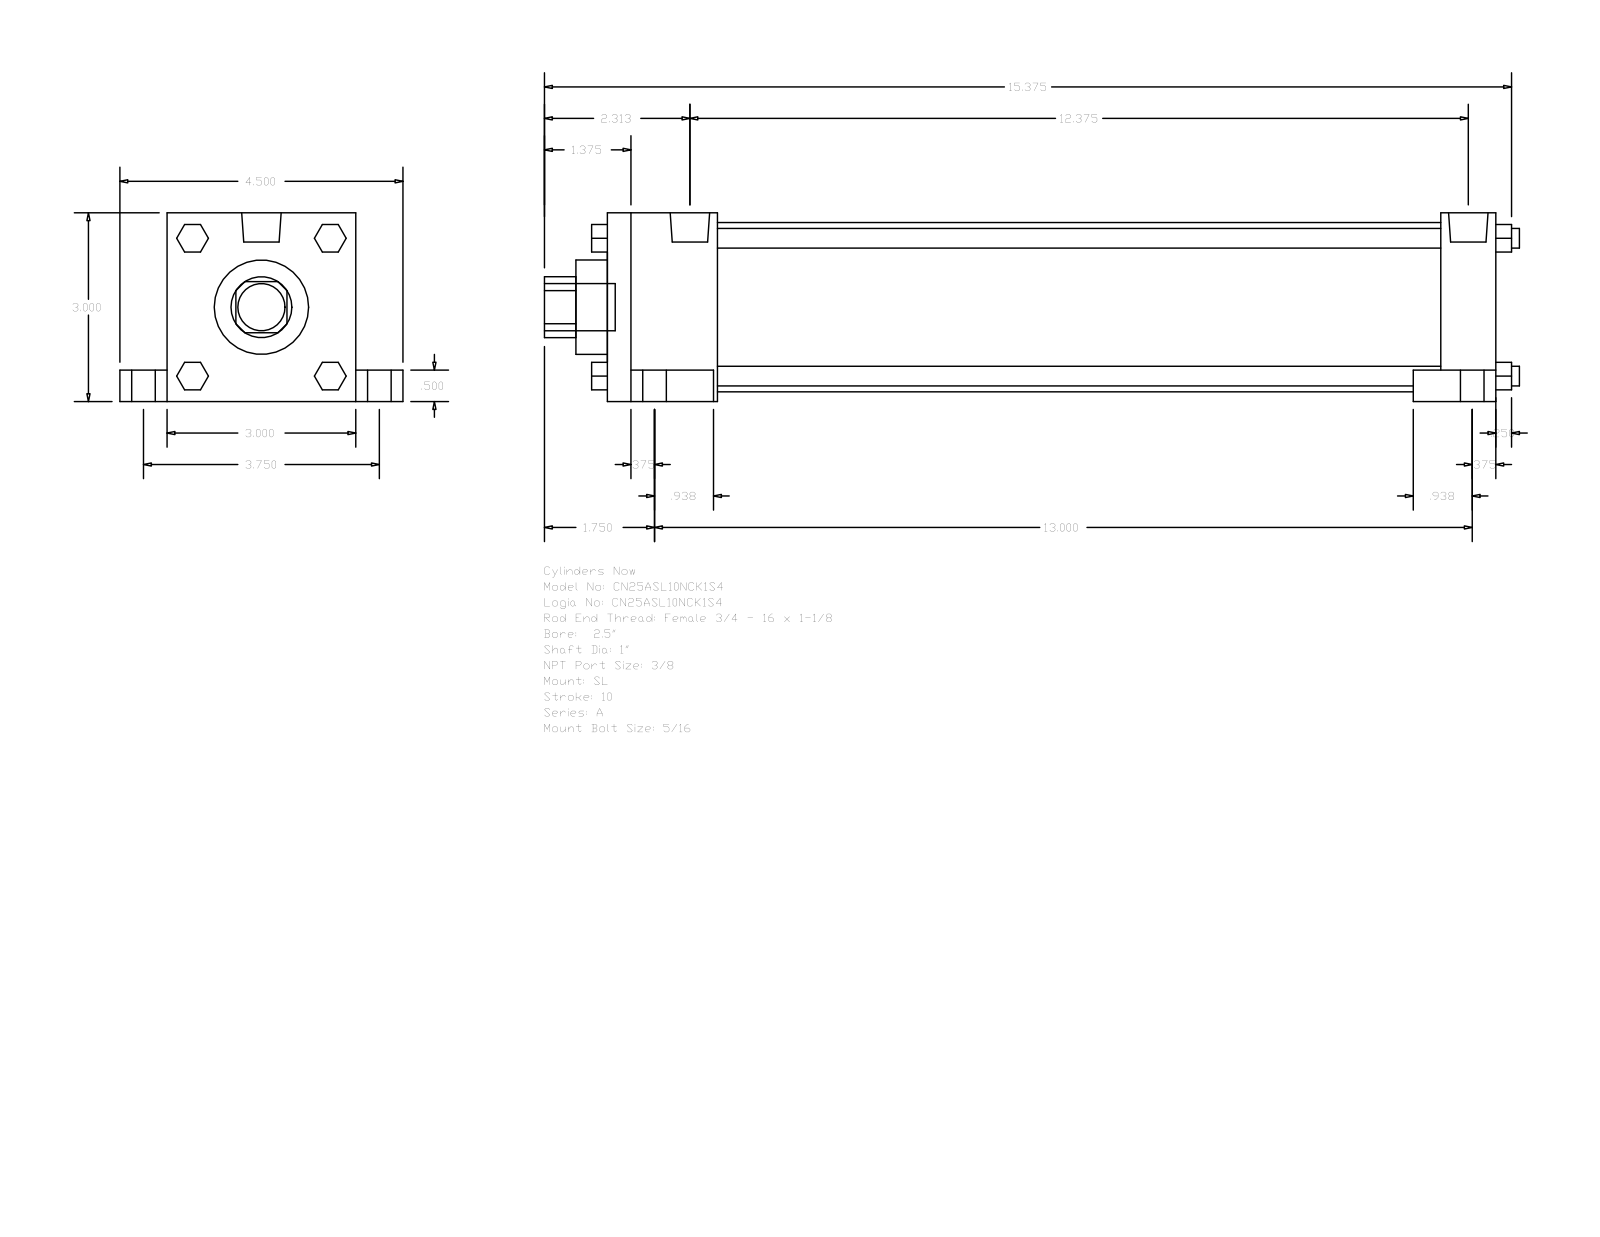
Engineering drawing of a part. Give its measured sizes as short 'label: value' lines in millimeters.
name: A_SL__0250_1
written by: GSSL Pune (CONFIG_CONTROL_DESIGN)
unit: mm
bodies: 0 solids, 148 faces (112 planar, 36 cylindrical, 0 other)
size: 393.7 × 114.3 × 76.2
holes: 1× ⌀25.4, 1× ⌀38.1, 1× ⌀68.33
bosses: 4× ⌀15.88, 4× ⌀9.53, 4× ⌀7.94, 4× ⌀5.56, 2× ⌀15.93, 1× ⌀19.05
rounds: 1× R12.29
face distances: 76.2, 358.78, 12.7, 44.45, 314.33, 336.55, 292.1, 22.23, 19.05, 63.5
